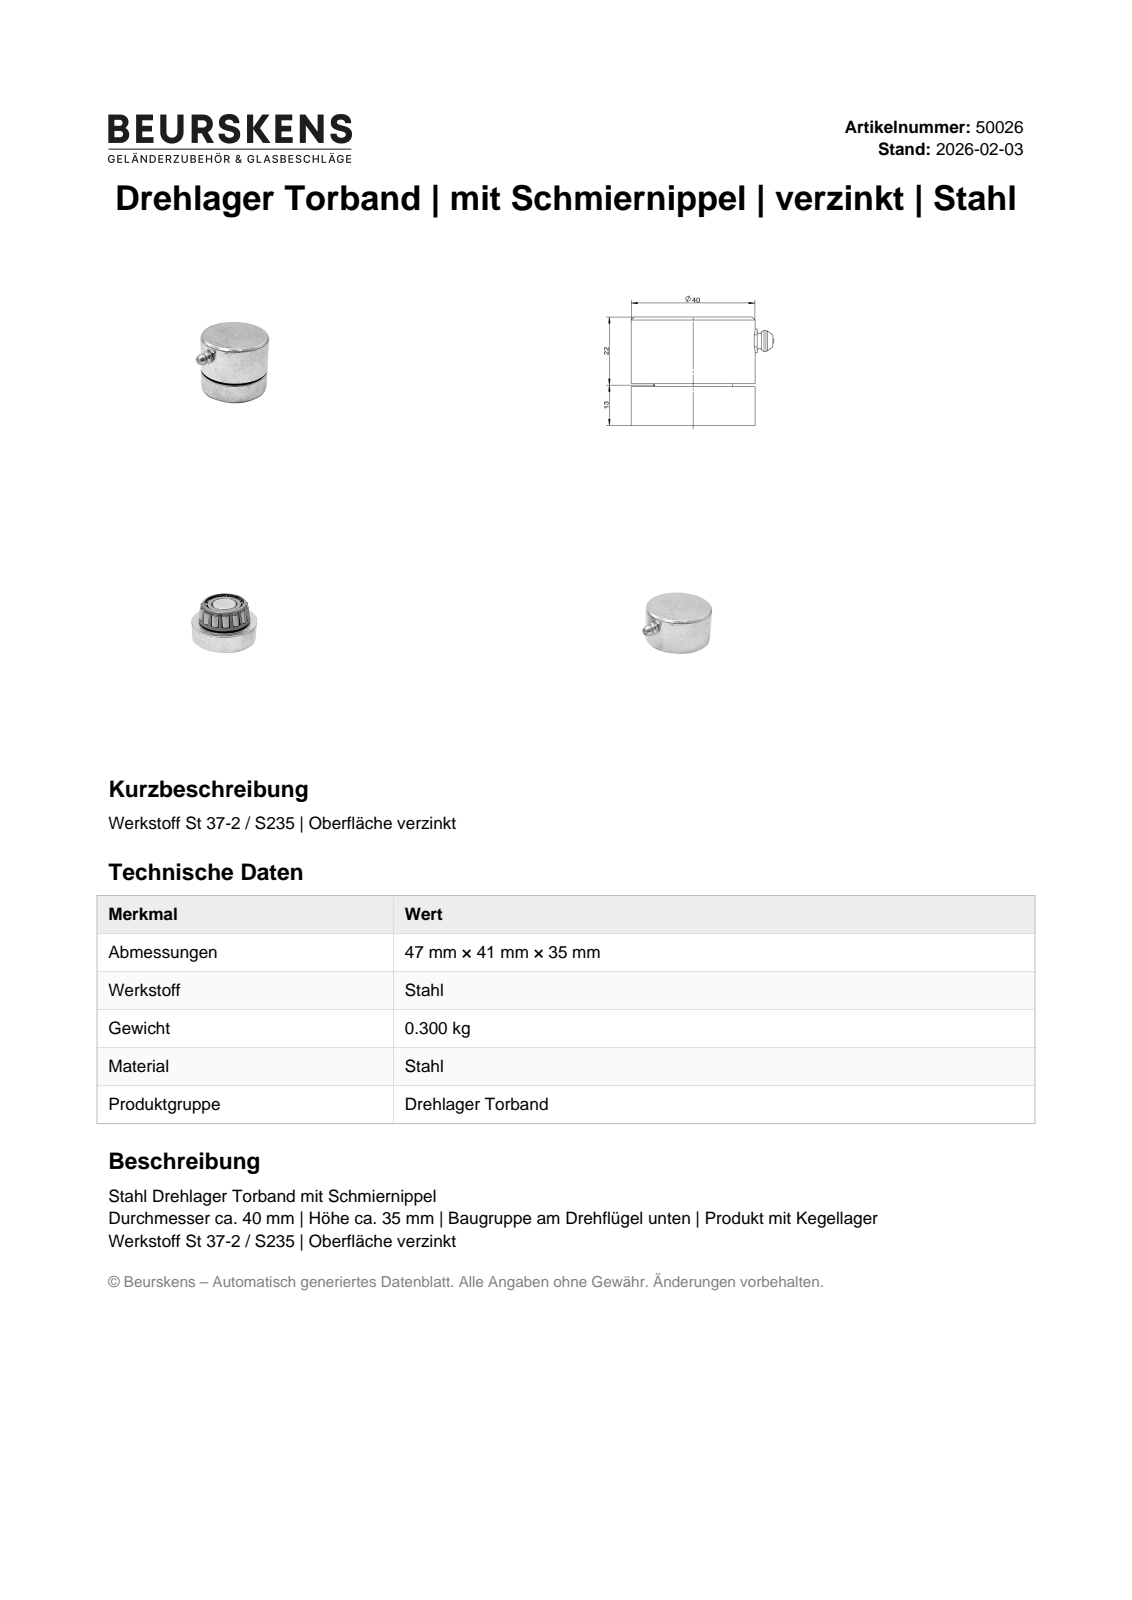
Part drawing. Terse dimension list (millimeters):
name: 50026; Boden; SKF_A 4059_A 4138; A 4059_A 4138_ir (+4 more)
written by: Autodesk Inventor 2023 (AUTOMOTIVE_DESIGN)
unit: mm
bodies: 20 solids, 105 faces (48 planar, 9 cylindrical, 48 other)
size: 46.02 × 40 × 35.32
volume: 38 047 mm³; area: 17 511 mm²
holes: 1× ⌀6, 1× ⌀14.99
bosses: 1× ⌀40, 1× ⌀25.3, 1× ⌀19.61, 1× ⌀15.52, 1× ⌀3
face distances: 35.32, 13, 22.32, 31.32, 18.32, 4, 13.32, 0.32, 18, 22
